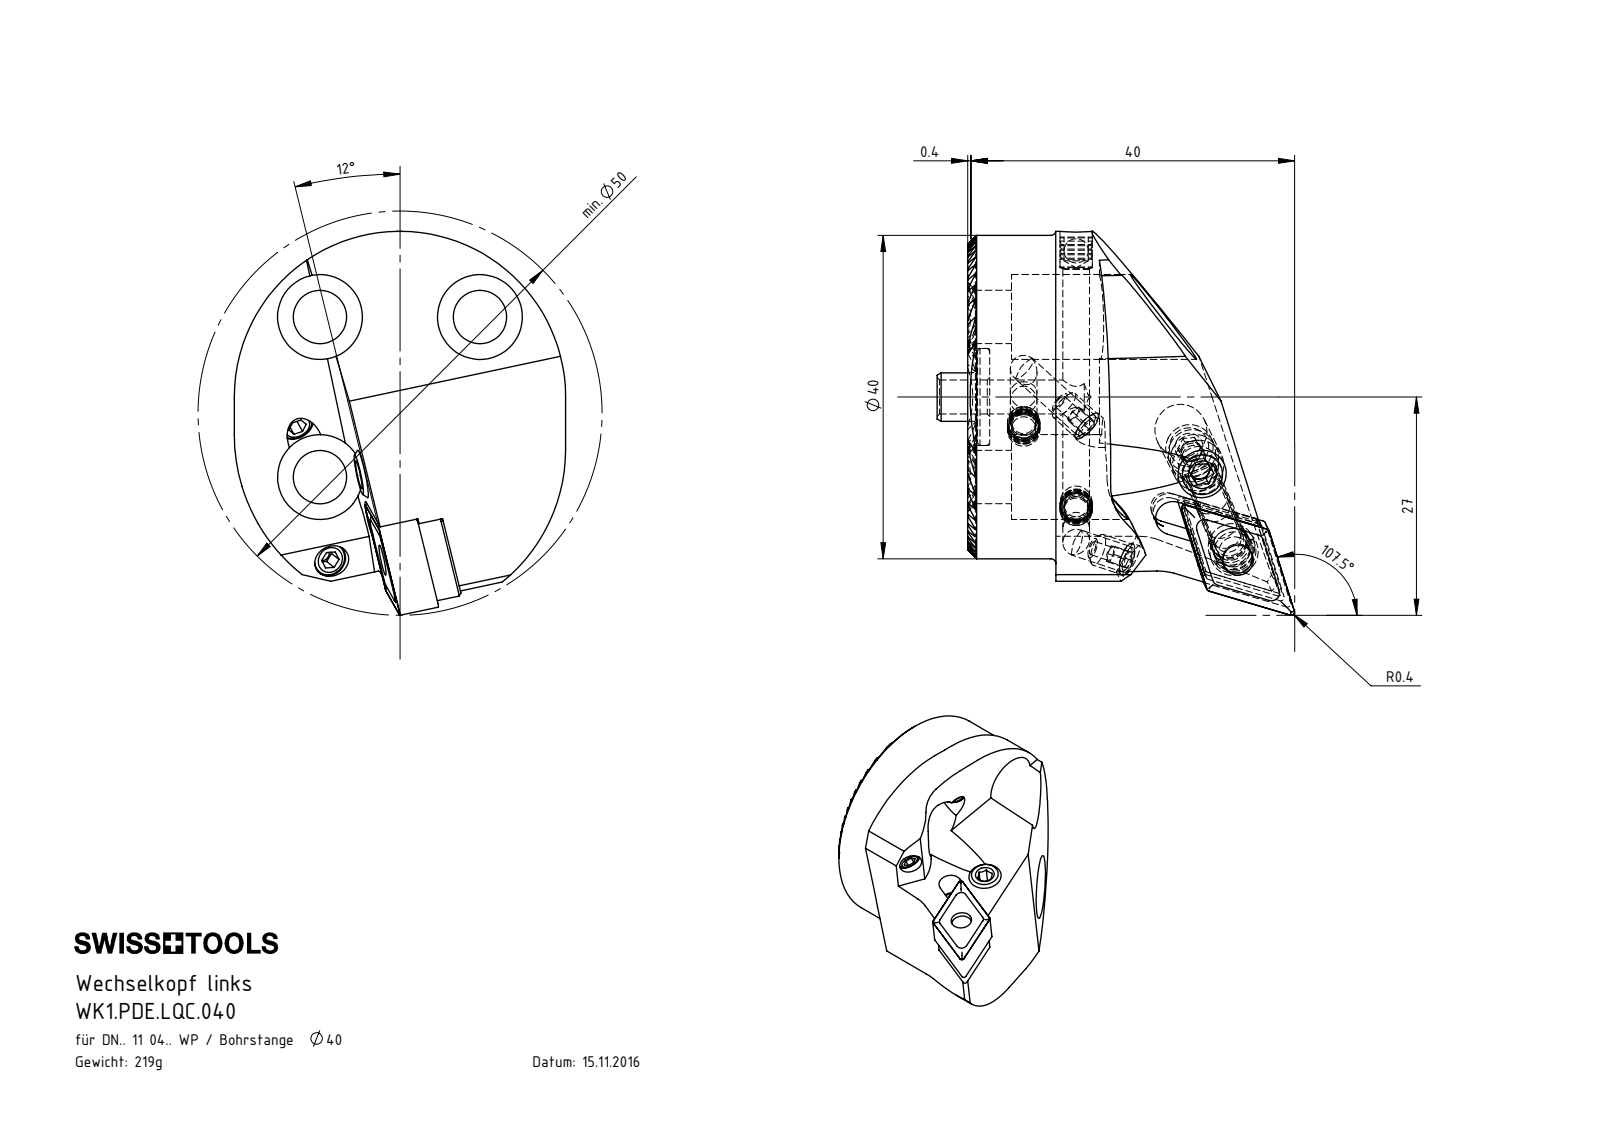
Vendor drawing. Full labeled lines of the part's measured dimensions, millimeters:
Part name (STEP PRODUCT): WDE-ER1.101.000; WKX-ER1.004.005_A_PreviewCfg; WK1-PDE.LQC.040_A; KVT_MB_600_040 (+6 more)
STEP written by: SolidWorks 2017 (AUTOMOTIVE_DESIGN)
Units: millimetres
Bodies: 15 solids, 506 faces (277 planar, 119 cylindrical, 110 other)
Overall size (bounding box): 47.5 × 44.25 × 41
Volume: 28 366 mm³ · Surface area: 13 316 mm²
Round holes (diameter × count): ⌀3.3 ×5, ⌀3 ×3, ⌀4.2 ×3, ⌀6.6 ×3, ⌀10.5 ×3, ⌀1.7 ×2, ⌀3.81 ×1, ⌀4 ×1, ⌀4.8 ×1, ⌀5 ×1, ⌀6.4 ×1, ⌀12 ×1
Round bosses / shafts (diameter × count): ⌀4 ×5, ⌀6 ×2, ⌀40 ×1, ⌀5.9 ×1, ⌀2.87 ×1
Partial cylindrical surfaces — rounded edges, fillets, slot ends (radius × count): R0.12 ×26, R0.4 ×8, R2.1 ×5, R7 ×2, R1.83 ×1, R1.85 ×1, R2.25 ×1, R2.35 ×1
Main face-to-face distances: 1.3, 2.6, 3.9, 12.99, 5.2, 11.69, 9.09, 10.39, 7.79, 7.8
Hole centre spacings: 14, 19.8, 11.79, 28
